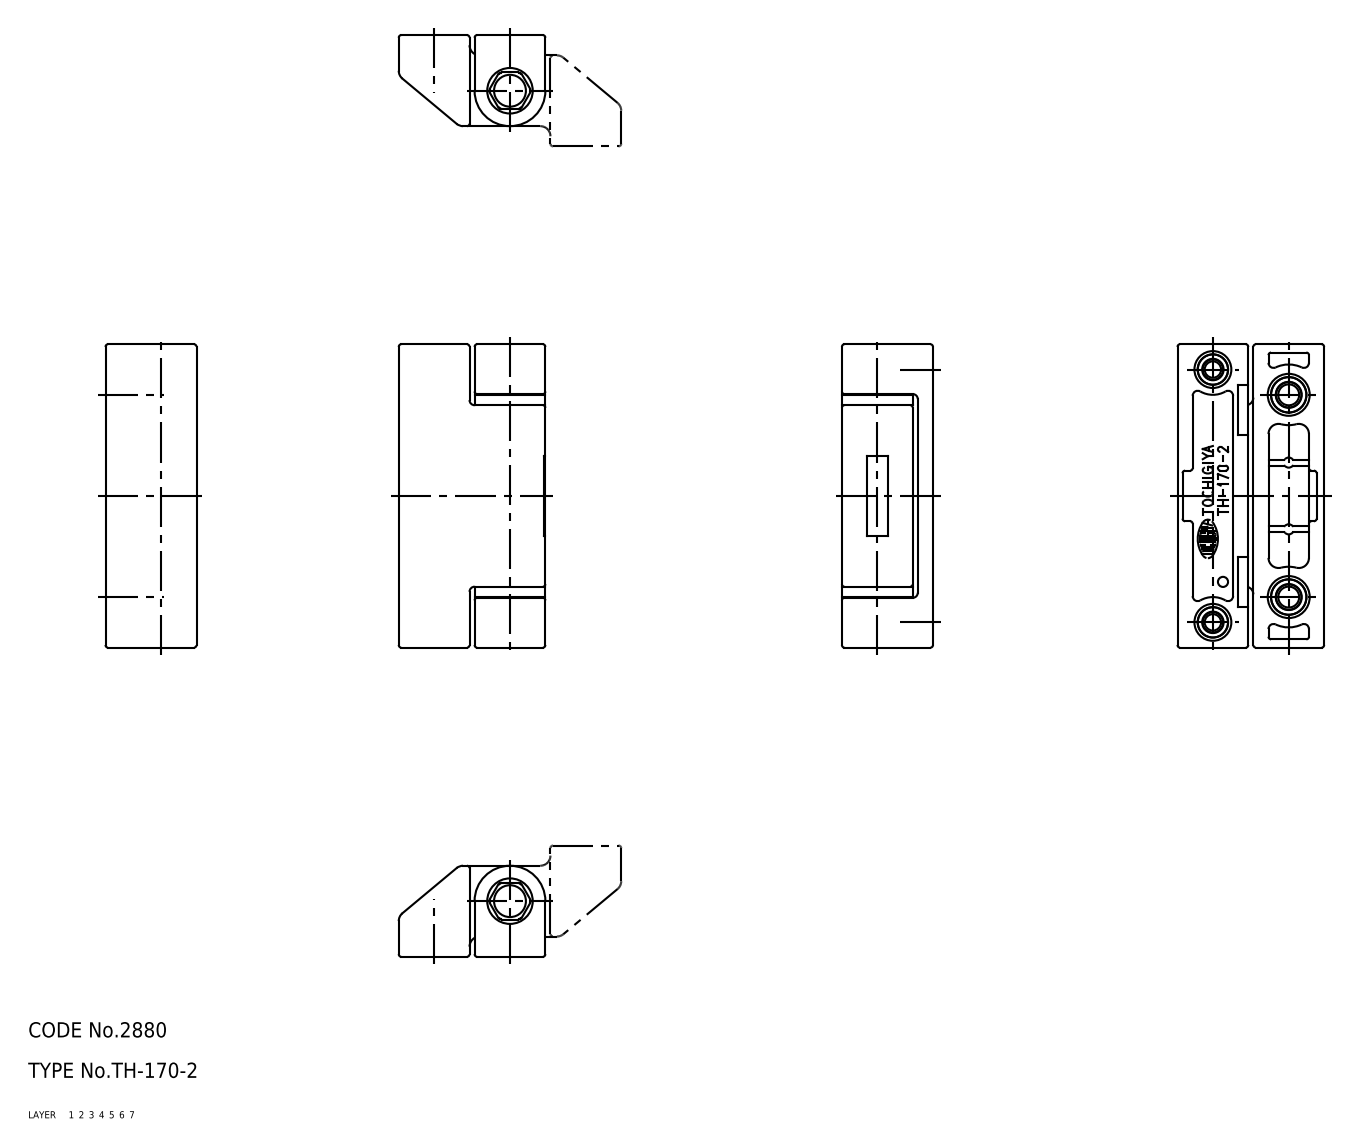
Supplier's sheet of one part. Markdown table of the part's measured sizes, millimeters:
| quantity | value |
| --- | --- |
| part name | 固定ブラケット; 可動ブラケット; TH_170_2 |
| STEP written by | SolidWorks 2015 (AUTOMOTIVE_DESIGN) |
| units | millimeters |
| bodies | 2 solids, 427 faces (97 planar, 211 cylindrical, 119 other) |
| overall size | 60 × 29 × 18 |
| volume | 21 977 mm³ |
| surface area | 11 846 mm² |
| round holes (diameter × count) | 3.25 × 2, 4.14 × 2, 7.3 × 2, 8.3 × 2, 4.85 × 1, 5.9 × 1 |
| round bosses / shafts (diameter × count) | 14 × 1, 5.19 × 1 |
| partial cylindrical surfaces (radius × count) | 0.5 × 43, 1 × 15, 0.2 × 8, 2 × 8, 5 × 2, 6 × 2, 4 × 1, 4.03 × 1 |
| main face-to-face distances | 3, 15, 14, 18, 1, 4, 11, 0.5, 2.5, 17.5 |
| hole center spacings | 15.81, 47.43, 40, 50 |
